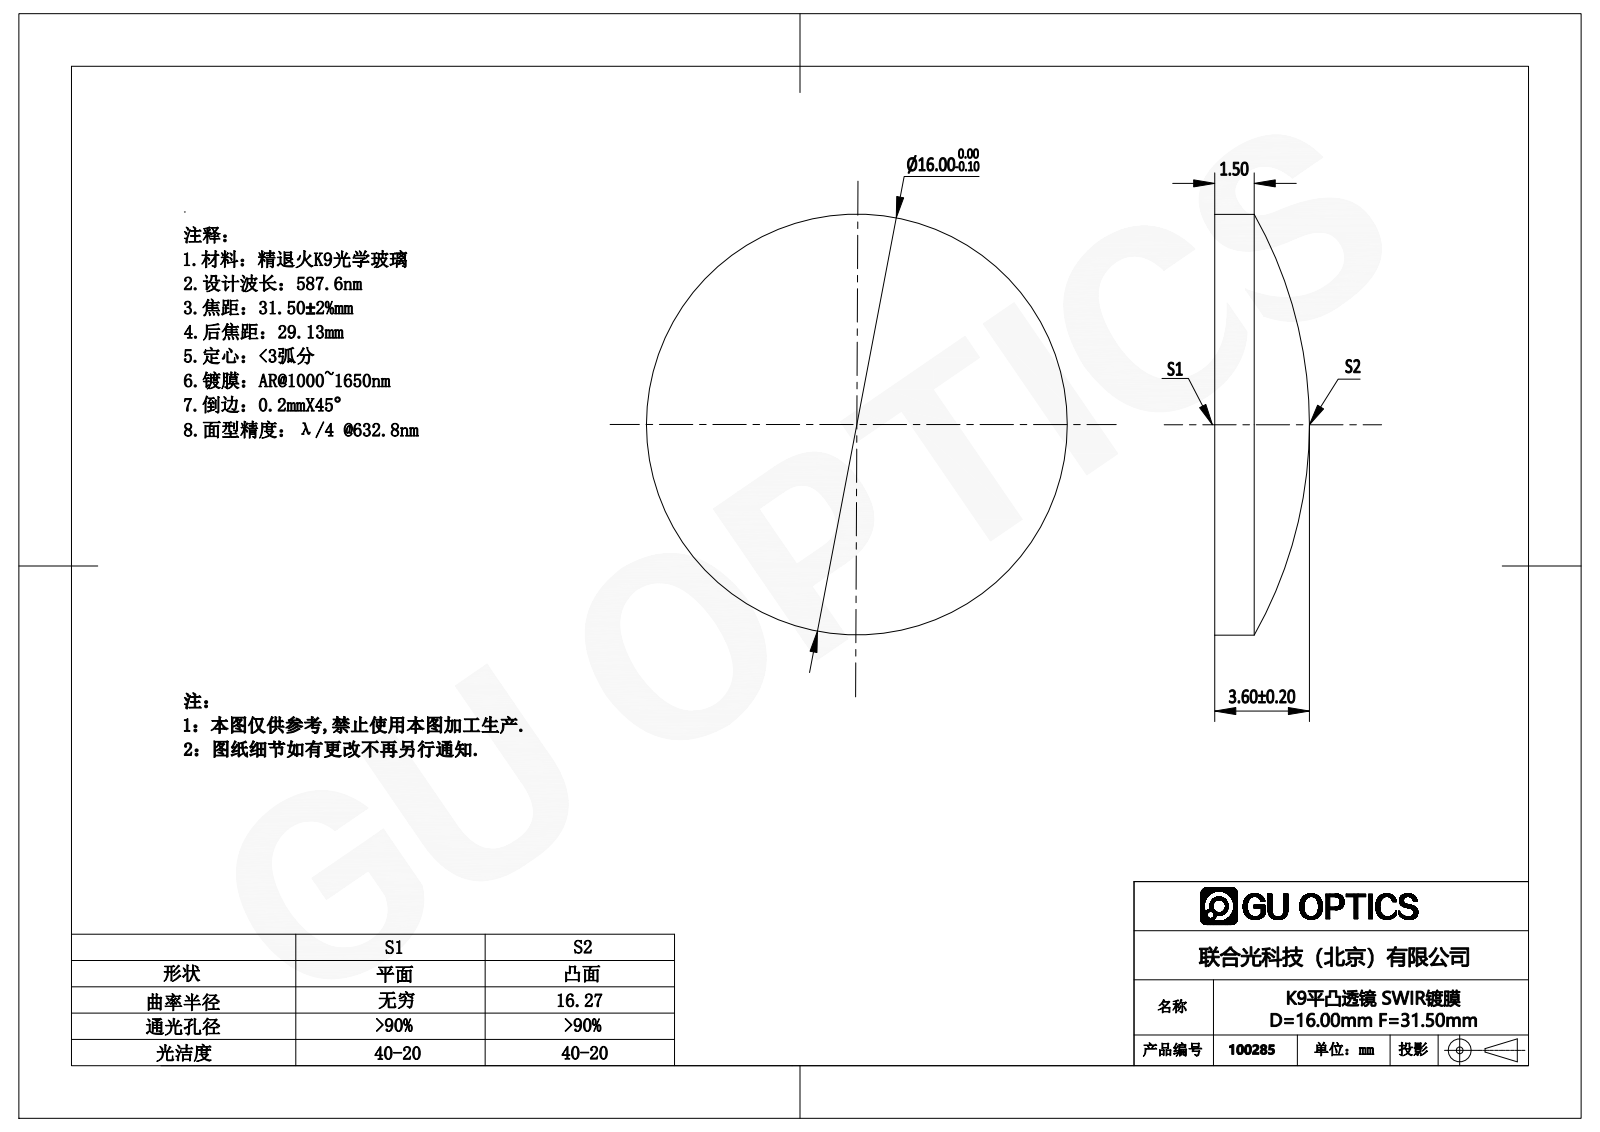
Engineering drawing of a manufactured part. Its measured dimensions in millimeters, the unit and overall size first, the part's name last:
Units: millimetres
Overall size (bounding box): 16 × 16 × 3.6
Round bosses / shafts (diameter × count): ⌀16 ×1
Volume: 518 mm³ · Surface area: 491 mm²
Bodies: 1 solid, 5 faces (1 planar, 2 cylindrical, 2 other)
Part name (STEP PRODUCT): 100113
STEP written by: SolidWorks 2016 (AUTOMOTIVE_DESIGN)
